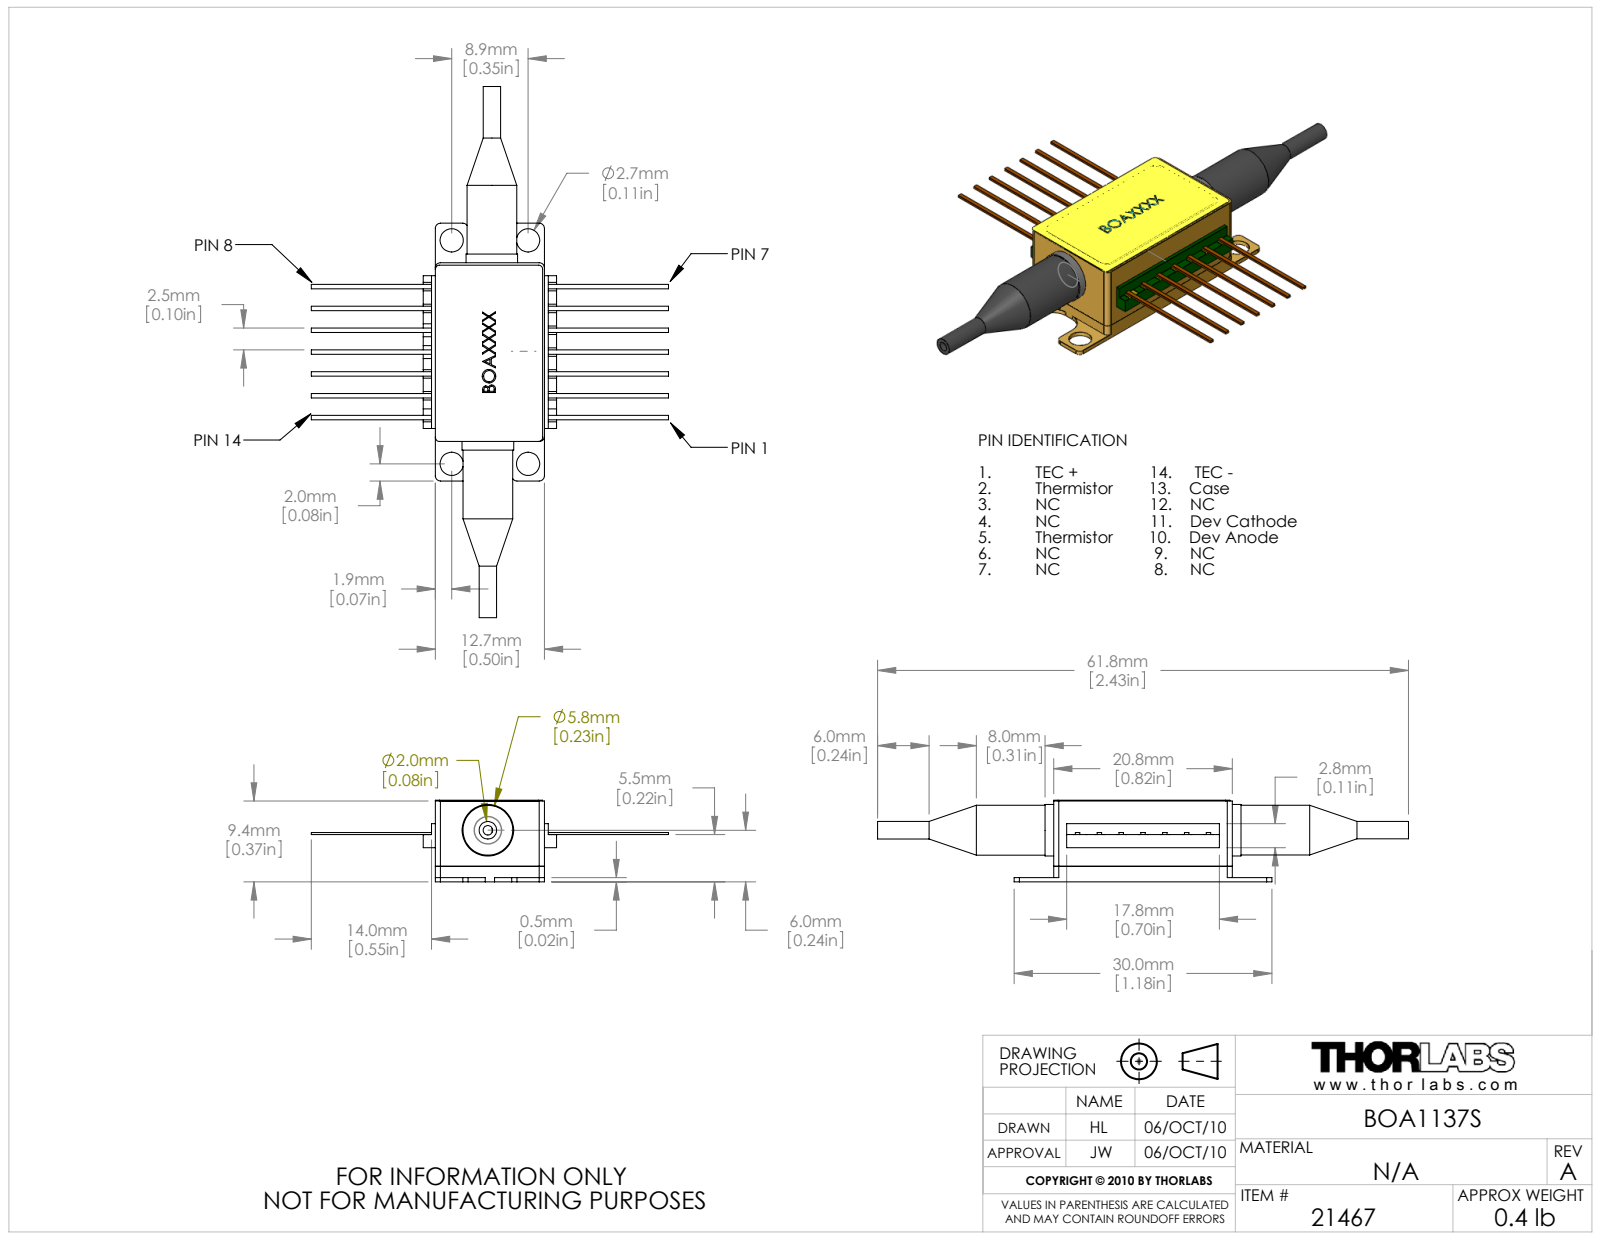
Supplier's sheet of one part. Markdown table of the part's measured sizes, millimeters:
| quantity | value |
| --- | --- |
| part name | 21467 BOA1137S |
| STEP written by | SolidWorks 2009 (AUTOMOTIVE_DESIGN) |
| units | millimeters |
| bodies | 0 solids, 268 faces (202 planar, 48 cylindrical, 18 other) |
| overall size | 61.8 × 41.6 × 9.5 |
| round holes (diameter × count) | 2.7 × 4, 1.1 × 2 |
| round bosses / shafts (diameter × count) | 6 × 2, 5.8 × 2, 2.04 × 2 |
| partial cylindrical surfaces (radius × count) | 0.6 × 12, 0.5 × 4, 2 × 4 |
| main face-to-face distances | 9.51, 12.7, 3.97, 5.54, 5.5, 1.53, 4.01, 0.5, 5.75, 1.78 |
| hole center spacings | 8.9, 26, 27.48, 0.47 |
